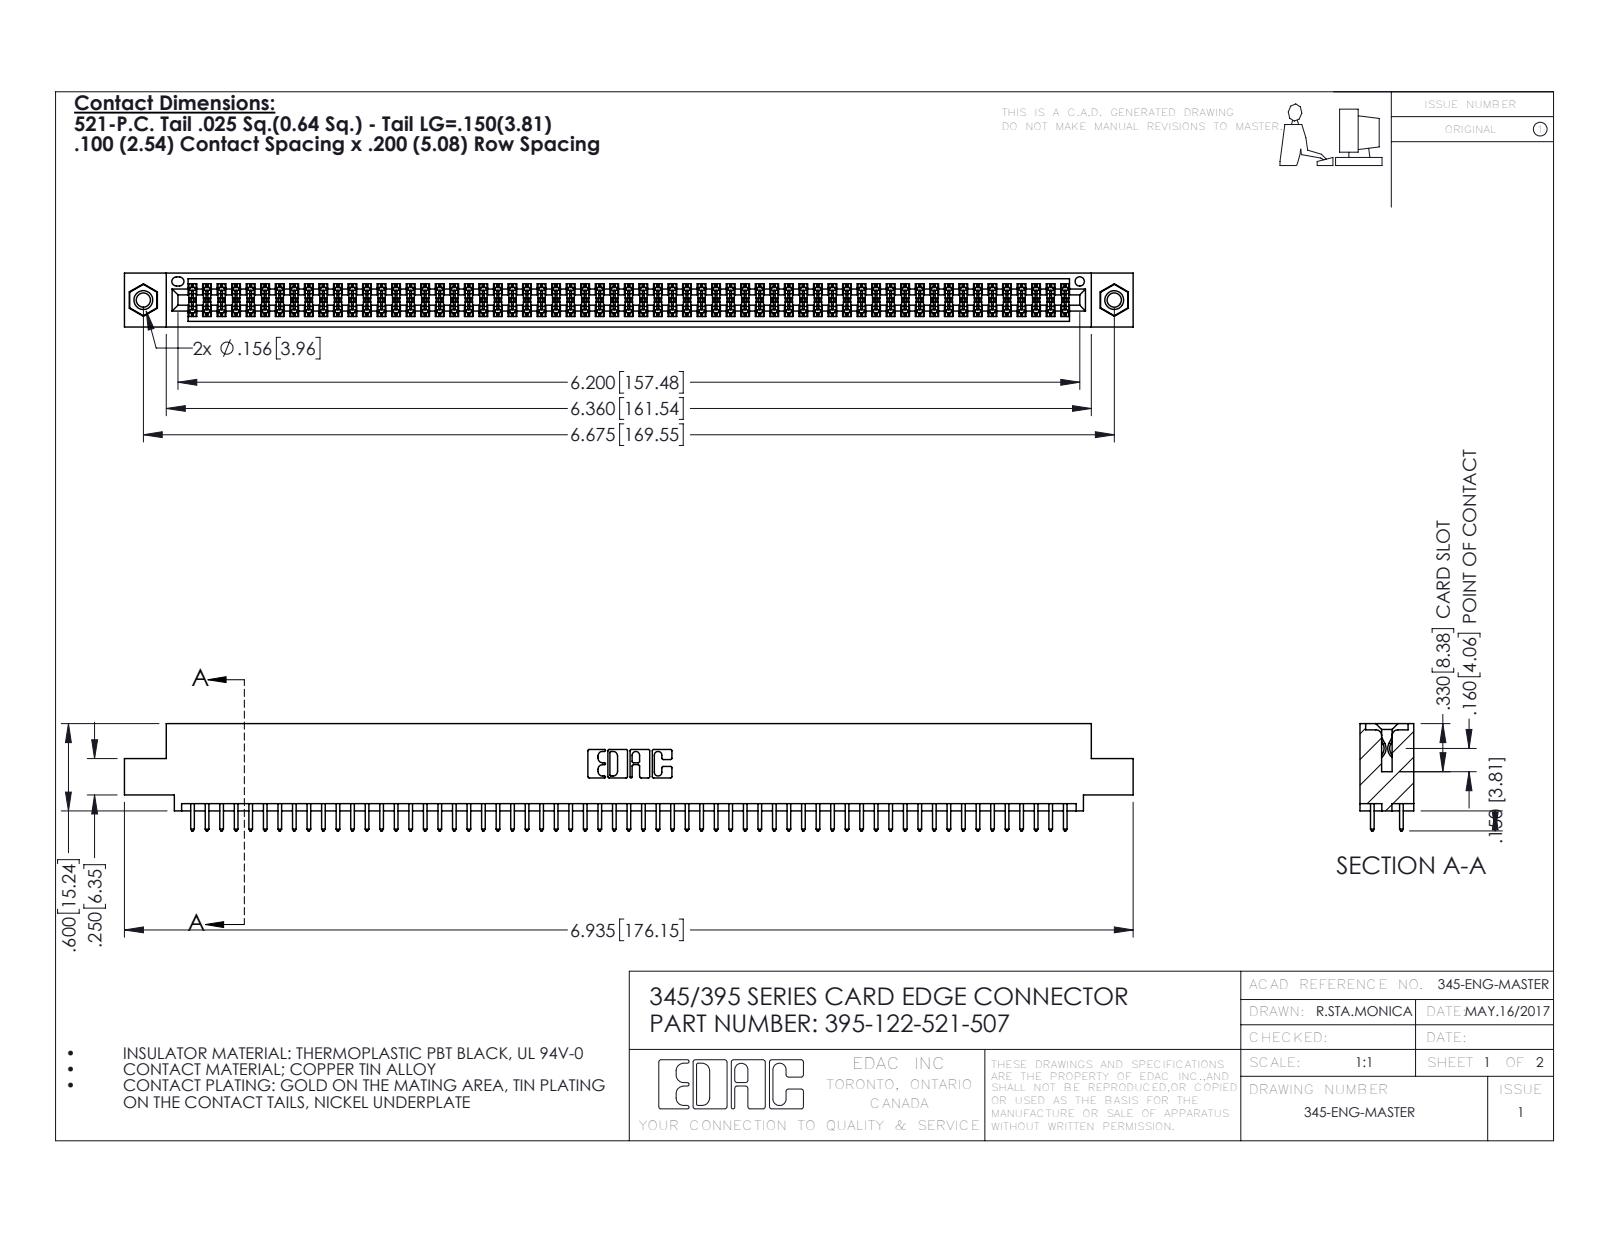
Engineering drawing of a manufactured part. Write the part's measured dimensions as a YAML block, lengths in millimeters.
part_name: "345-292-001_345-293-121; 345-250-001_345-250-005-103; 395-122-521-507; 345 Part_0.110 Offset - 0.156 Dia-TI"
step_written_by: "SolidWorks 2016 (CONFIG_CONTROL_DESIGN)"
units: millimeters
bodies: {solids: 125, faces: 6290, planar: 4142, cylindrical: 2132, other: 16}
overall_size: [176.1, 18.7, 9.4]
volume: 17160
surface_area: 25520
round_holes:
  - {diameter: 2.5, count: 2}
  - {diameter: 3.2, count: 2}
  - {diameter: 4, count: 2}
  - {diameter: 1.6, count: 1}
round_bosses_or_shafts:
  - {diameter: 3.9, count: 2}
partial_cylinders:
  - {radius: 0.2, count: 183}
  - {radius: 0.3, count: 122}
  - {radius: 0.3, count: 22}
  - {radius: 0.2, count: 6}
  - {radius: 0.8, count: 6}
  - {radius: 0.7, count: 3}
  - {radius: 0.4, count: 2}
  - {radius: 0.5, count: 2}
face_to_face_distances: [1.8, 7.6, 5.1, 2.5, 6.9, 0.6, 9.4, 5.7, 4.4, 3.8]
hole_center_spacings: [6.9, 163.6, 169.5]
